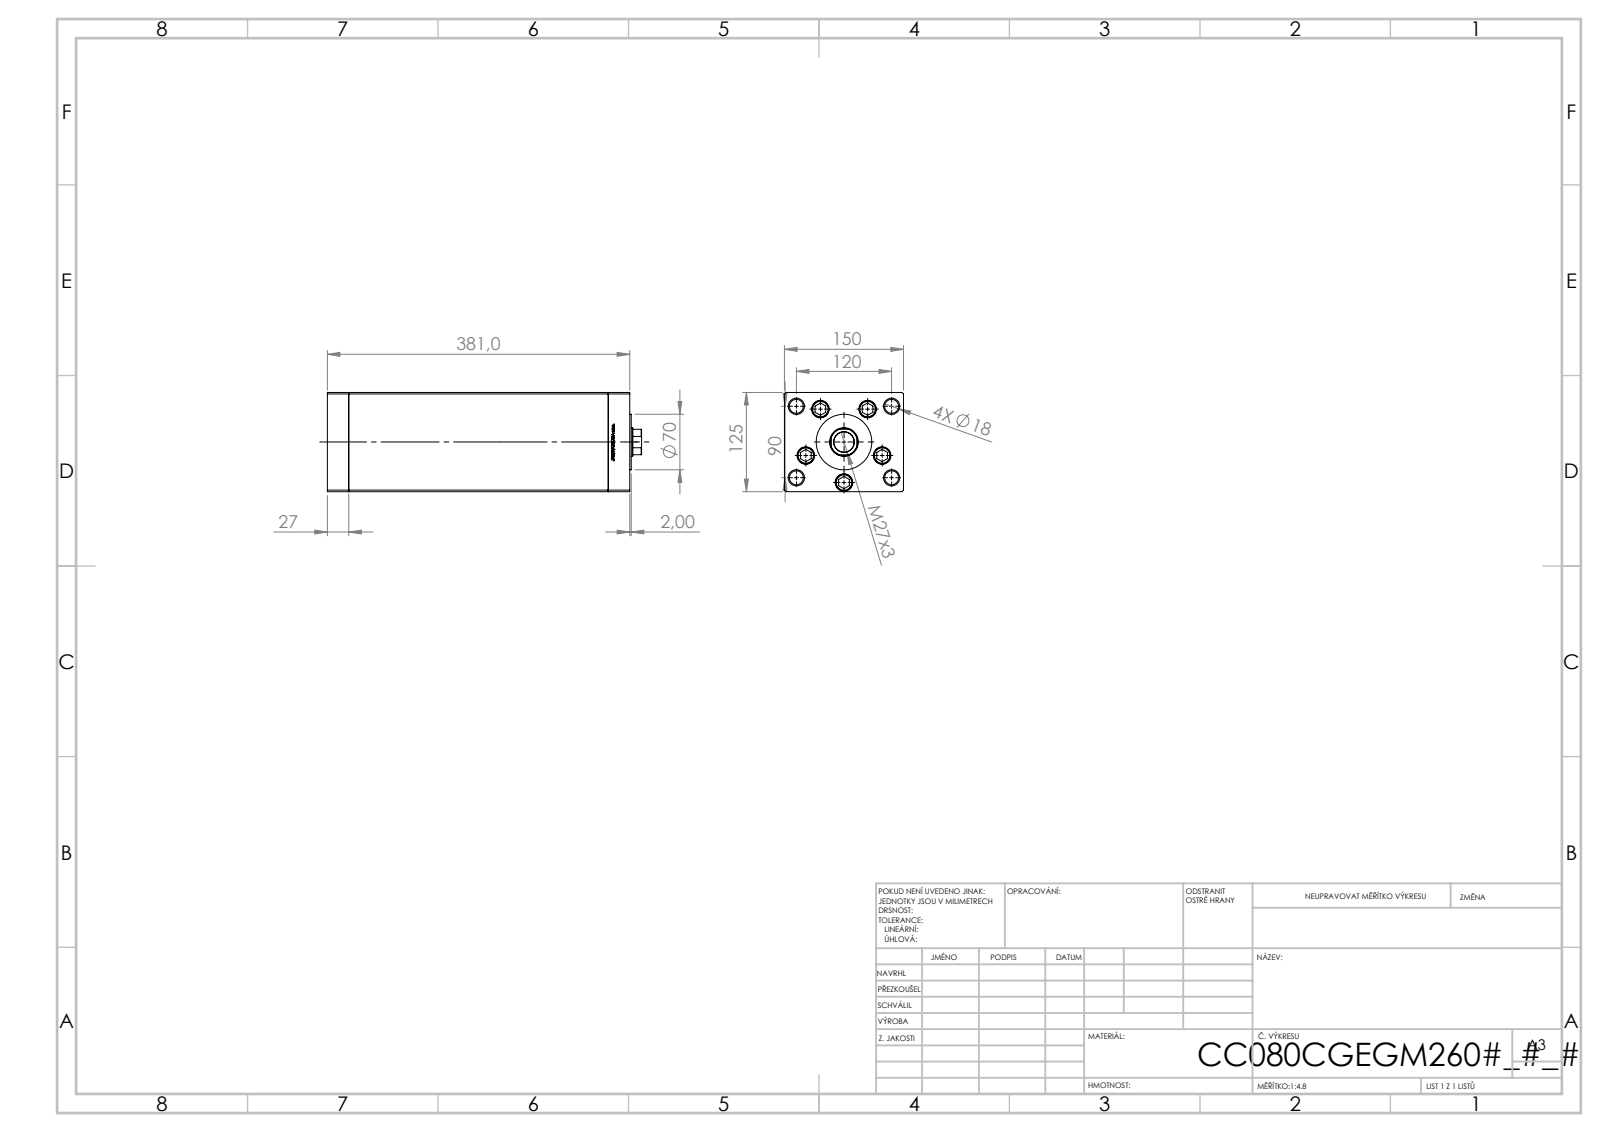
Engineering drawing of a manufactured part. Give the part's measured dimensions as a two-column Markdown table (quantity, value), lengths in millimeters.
| quantity | value |
| --- | --- |
| part name | V220C BACK_C; V220C_VC_C; V220C FRONT; ALLEN BOLT (+1 more) |
| STEP written by | SolidWorks 2019 (CONFIG_CONTROL_DESIGN) |
| units | millimeters |
| bodies | 13 solids, 1163 faces (542 planar, 159 cylindrical, 462 other) |
| overall size | 396 × 150 × 125 |
| volume | 5 727 000 mm³ |
| surface area | 552 610 mm² |
| round holes (diameter × count) | 17.5 × 9, 22 × 5, 16 × 4, 20.5 × 4, 21 × 1, 25.5 × 1, 36 × 1 |
| round bosses / shafts (diameter × count) | 8 × 5, 21 × 4, 80 × 1, 70 × 1 |
| partial cylindrical surfaces (radius × count) | 0.93 × 2, 17.5 × 1 |
| main face-to-face distances | 125, 150, 27, 354, 327, 33.5, 6.5, 381, 347.5, 320.5 |
| hole center spacings | 51, 75, 30.43, 30.48, 58.89, 60.3, 61.25, 63.14 |
